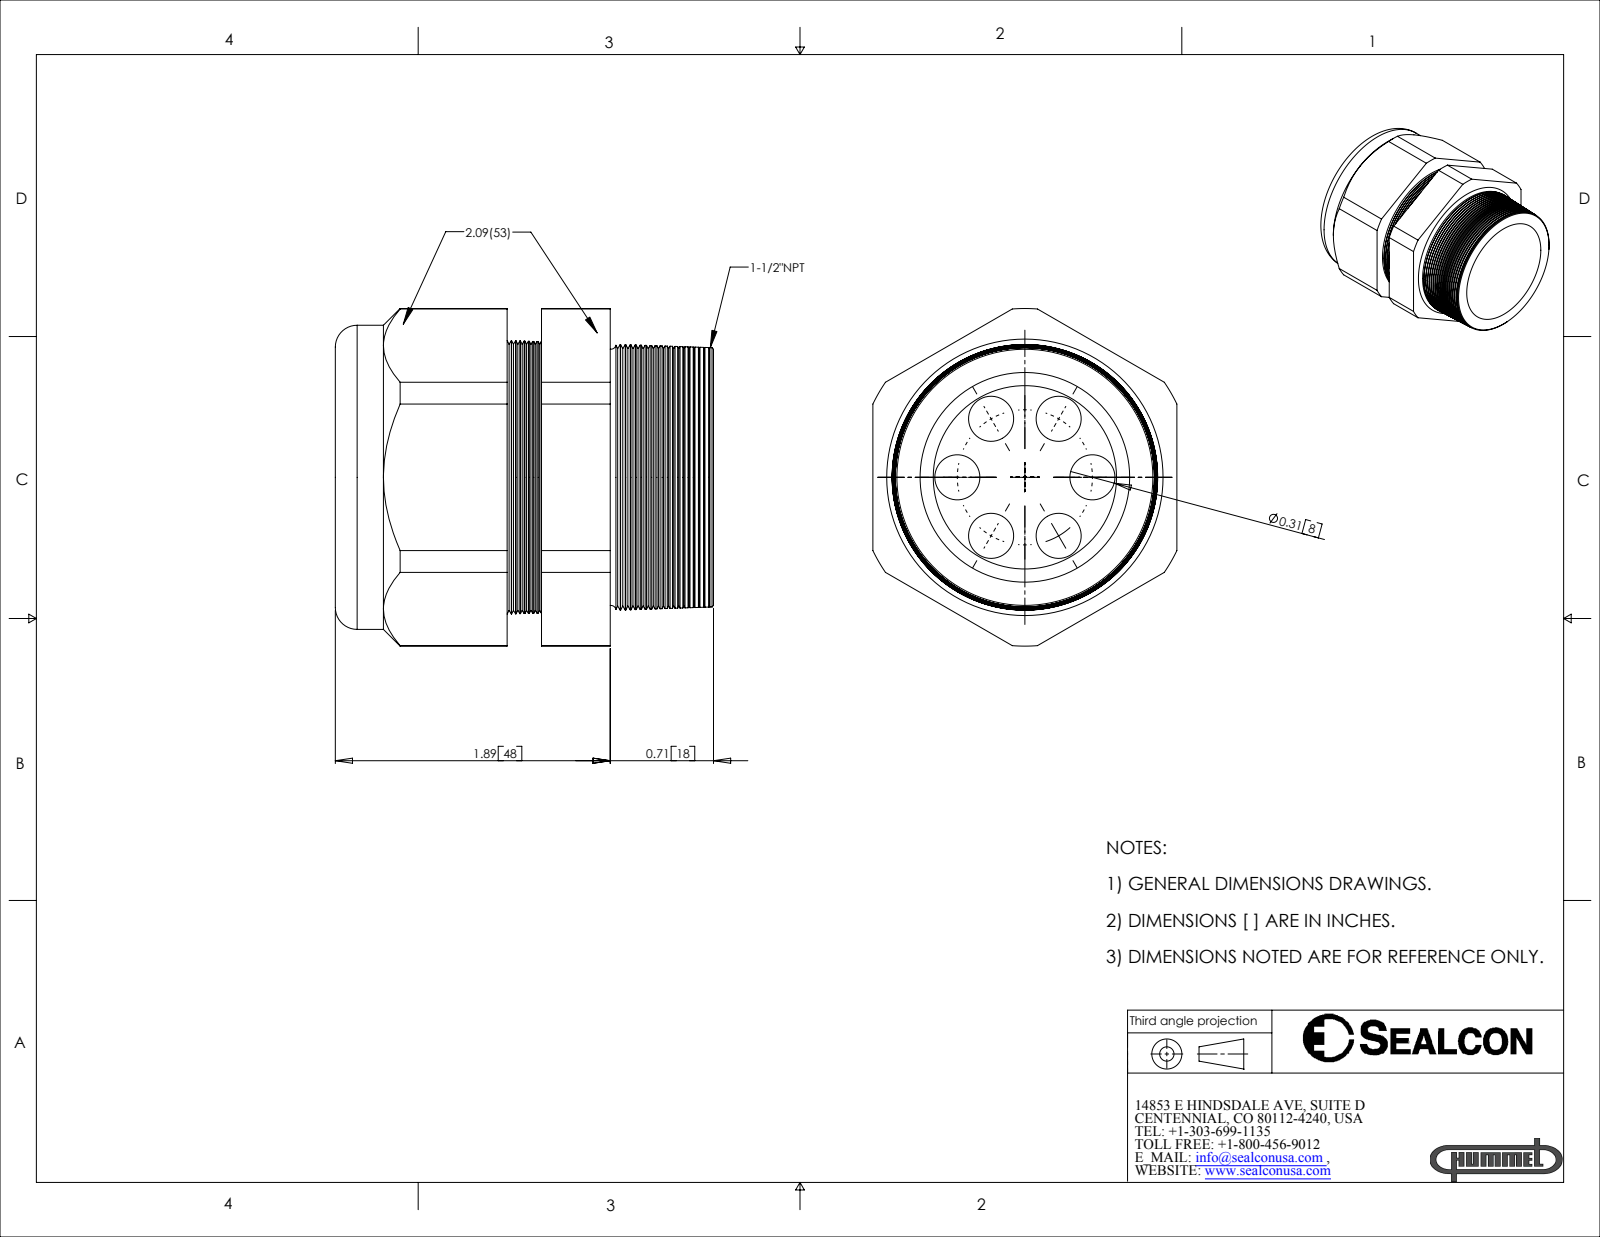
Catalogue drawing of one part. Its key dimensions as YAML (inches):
part_name: "CD36N3-BK"
step_written_by: "SolidWorks 2007 (CONFIG_CONTROL_DESIGN)"
units: inches
bodies: {solids: 2, faces: 235, planar: 21, cylindrical: 32, other: 182}
overall_size: [2.6, 2.32, 2.09]
volume: 5.355
surface_area: 43.68
round_holes:
  - {diameter: 0.31, count: 6}
  - {diameter: 1.24, count: 1}
  - {diameter: 1.26, count: 1}
round_bosses_or_shafts:
  - {diameter: 2.09, count: 1}
partial_cylinders:
  - {radius: 1.16, count: 1}
face_to_face_distances: [2.09, 1.418, 1.181, 0.237, 1.89, 0.709, 0.472, 2.6, 1.419, 1.182]
hole_center_spacings: [0.464, 0.465, 0.804, 0.804, 0.928, 0.929]
